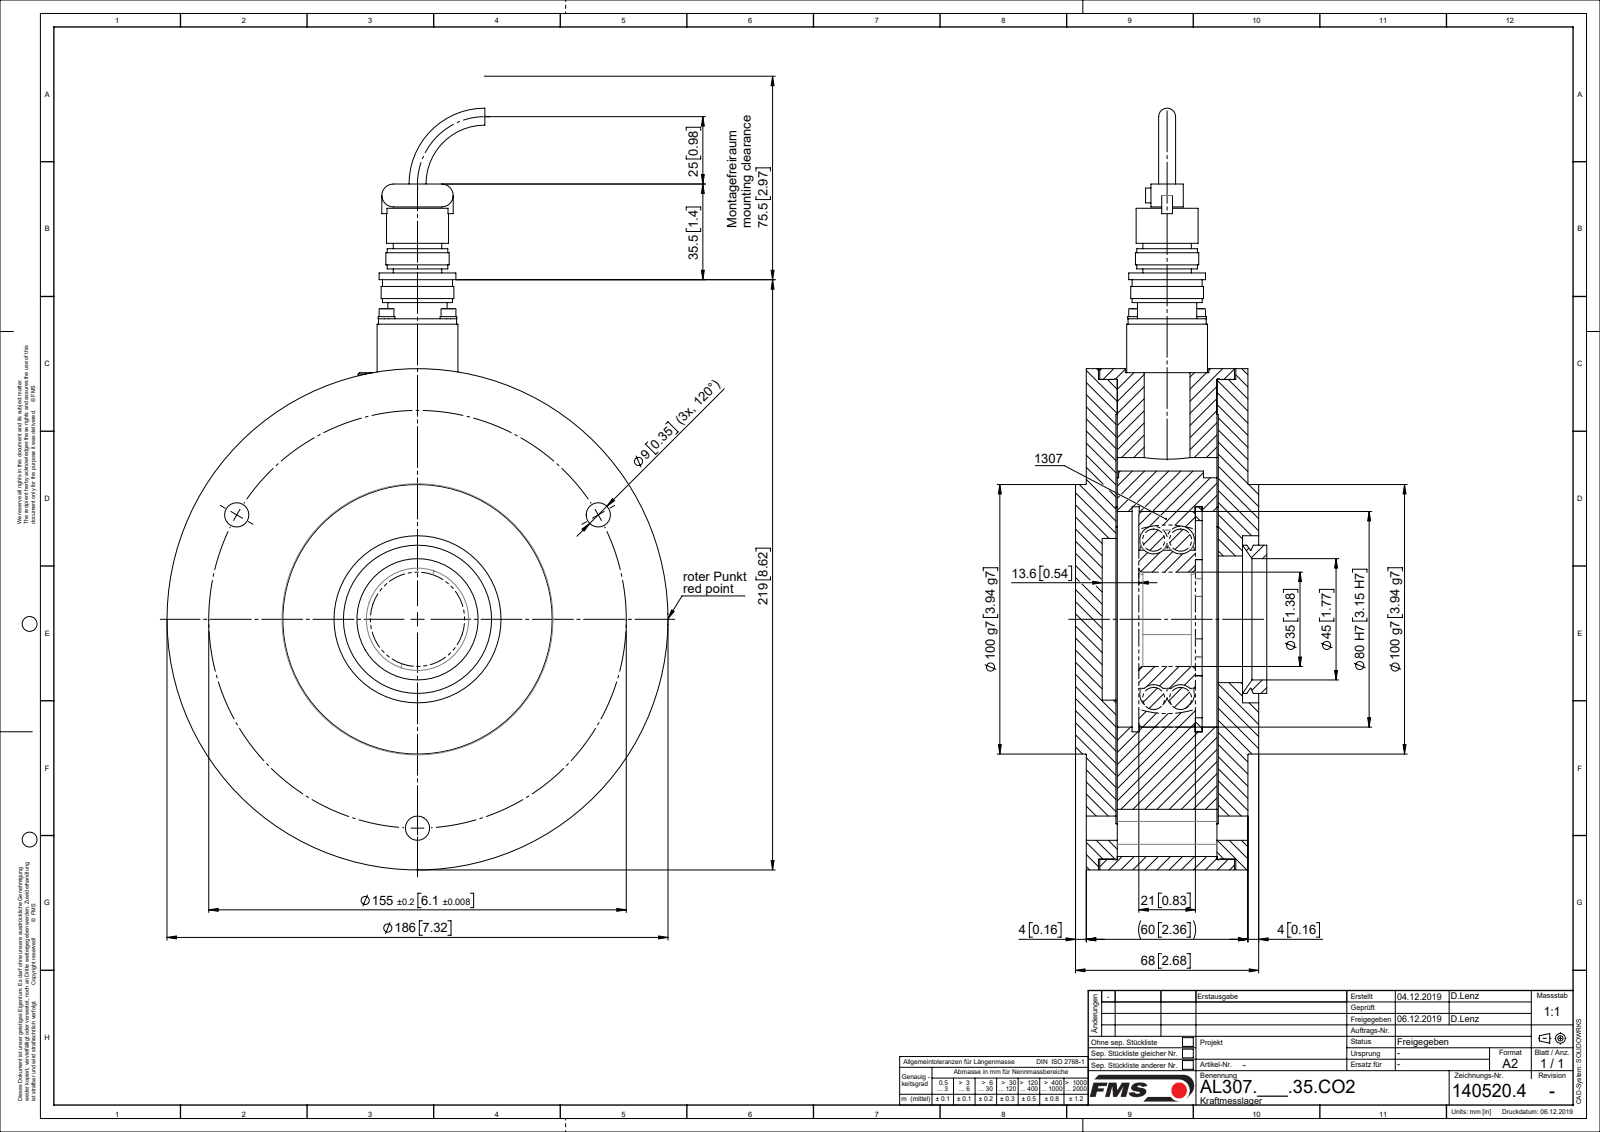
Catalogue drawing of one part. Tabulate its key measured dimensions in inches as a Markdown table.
| quantity | value |
| --- | --- |
| part name | 31101677_V-045A; 140520.4_stp; FLANSCHDOSE_14S-2P_4-POLIG; Si-Ring DIN472_D80x2.5 (+7 more) |
| STEP written by | SolidWorks 2018 (CONFIG_CONTROL_DESIGN) |
| units | inches |
| bodies | 45 solids, 474 faces (132 planar, 214 cylindrical, 128 other) |
| overall size | 11.128 × 7.323 × 2.795 |
| volume | 91.6 in³ |
| surface area | 439.7 in² |
| round holes (diameter × count) | 0.354 × 10, 0.098 × 4, 0.122 × 4, 0.134 × 4, 0.118 × 2, 0.157 × 1, 0.669 × 1, 0.906 × 1, 1.378 × 1, 1.772 × 1, 1.85 × 1, 2.362 × 1 |
| round bosses / shafts (diameter × count) | 0.217 × 6, 0.244 × 4, 0.118 × 4, 0.098 × 4, 7.323 × 1, 3.937 × 1, 2.165 × 1, 2.018 × 1 |
| partial cylindrical surfaces (radius × count) | 0.177 × 6, 0.004 × 4, 0.167 × 2, 0.193 × 2, 1.309 × 1 |
| main face-to-face distances | 0.453, 1.909, 0.02, 1.929, 0.433, 1.476, 1.457, 0.591, 2.362, 1.496 |
| hole center spacings | 0.64, 0.906, 2.657, 3.758, 1.656, 3.051, 3.287, 5.285 |
